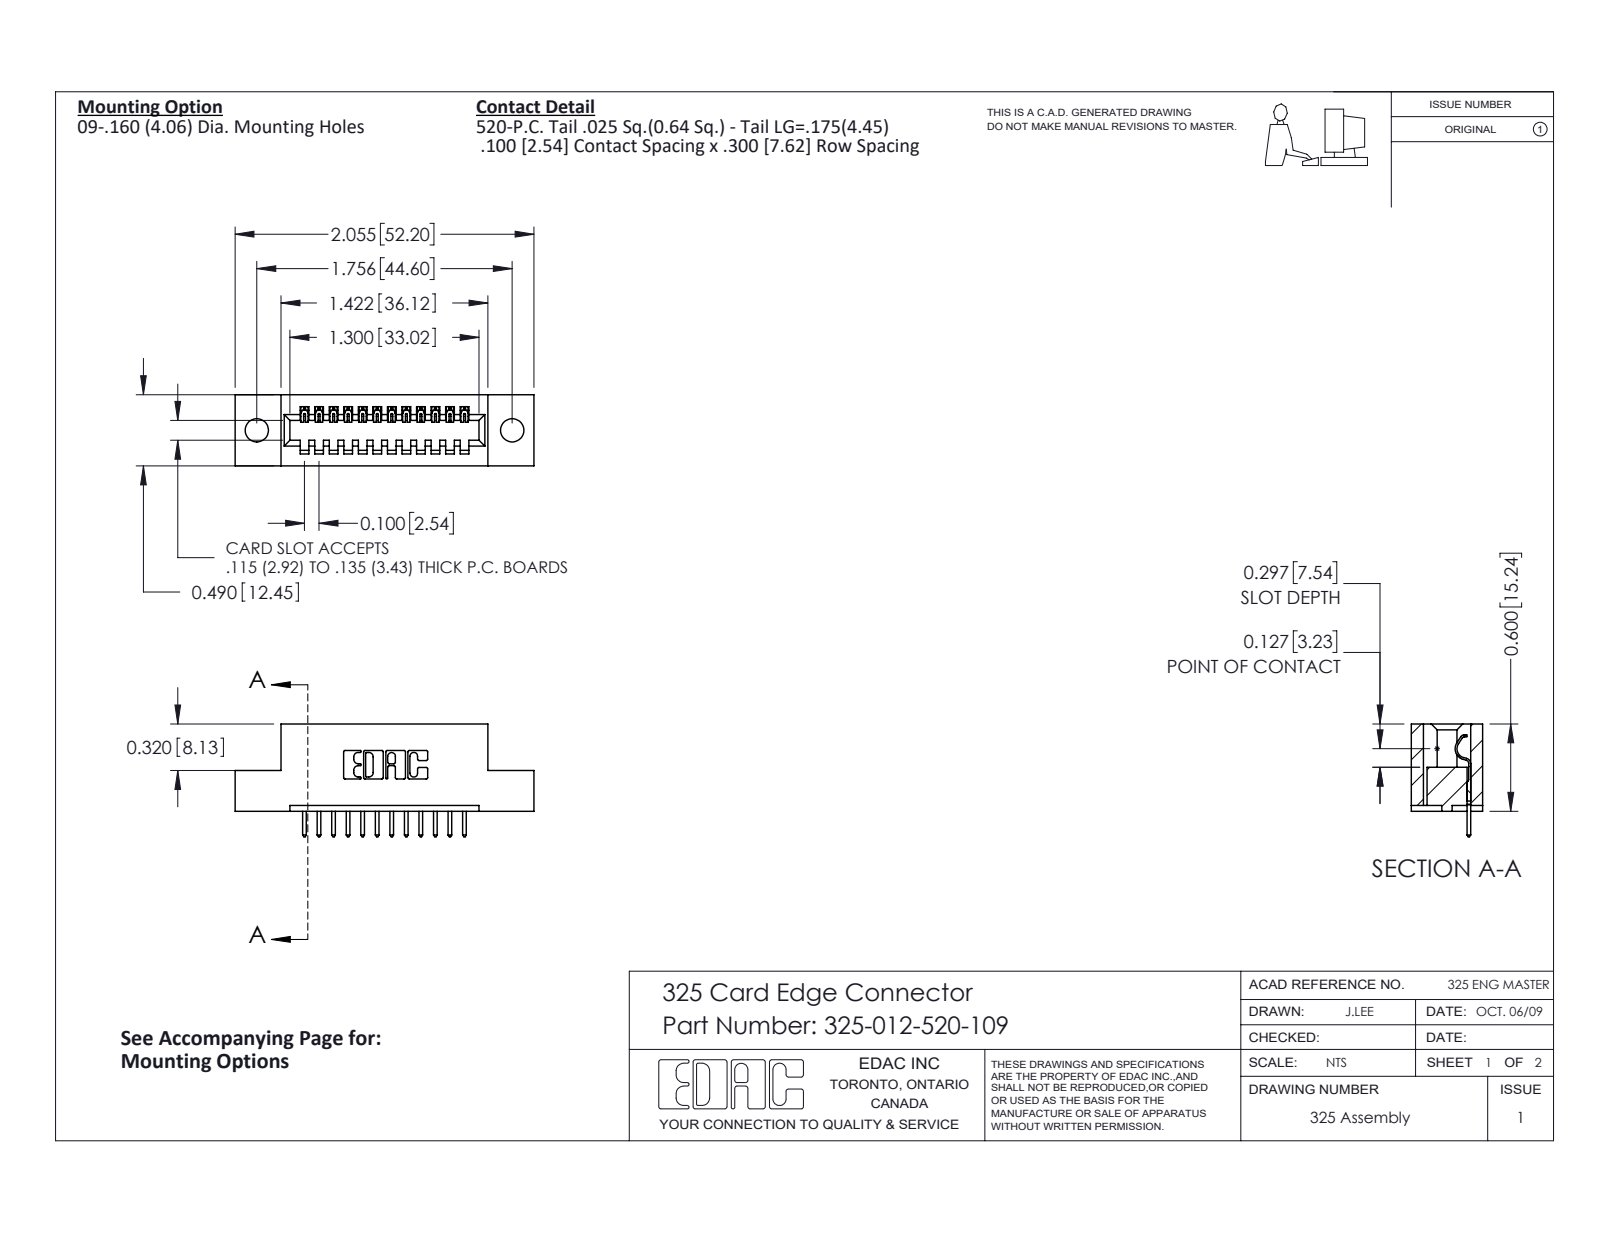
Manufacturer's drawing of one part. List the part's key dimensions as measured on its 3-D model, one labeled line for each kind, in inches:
Part name (STEP PRODUCT): 325 Part_.160 TH; 325-292-001_325-293-120; 325-012-520-109
STEP written by: SolidWorks 2016 (CONFIG_CONTROL_DESIGN)
Units: inches
Bodies: 13 solids, 810 faces (574 planar, 236 cylindrical, 0 other)
Overall size (bounding box): 2.055 × 0.775 × 0.49
Volume: 0.374 in³ · Surface area: 9.232 in²
Round holes (diameter × count): ⌀0.16 ×2
Partial cylindrical surfaces — rounded edges, fillets, slot ends (radius × count): R0.006 ×24, R0.01 ×24, R0.01 ×22, R0.007 ×6, R0.031 ×6, R0.026 ×3, R0.014 ×1, R0.022 ×1
Main face-to-face distances: 0.3, 0.083, 0.407, 0.49, 0.04, 0.1, 0.2, 0.6, 0.4, 0.107
Hole centre spacings: 1.756
